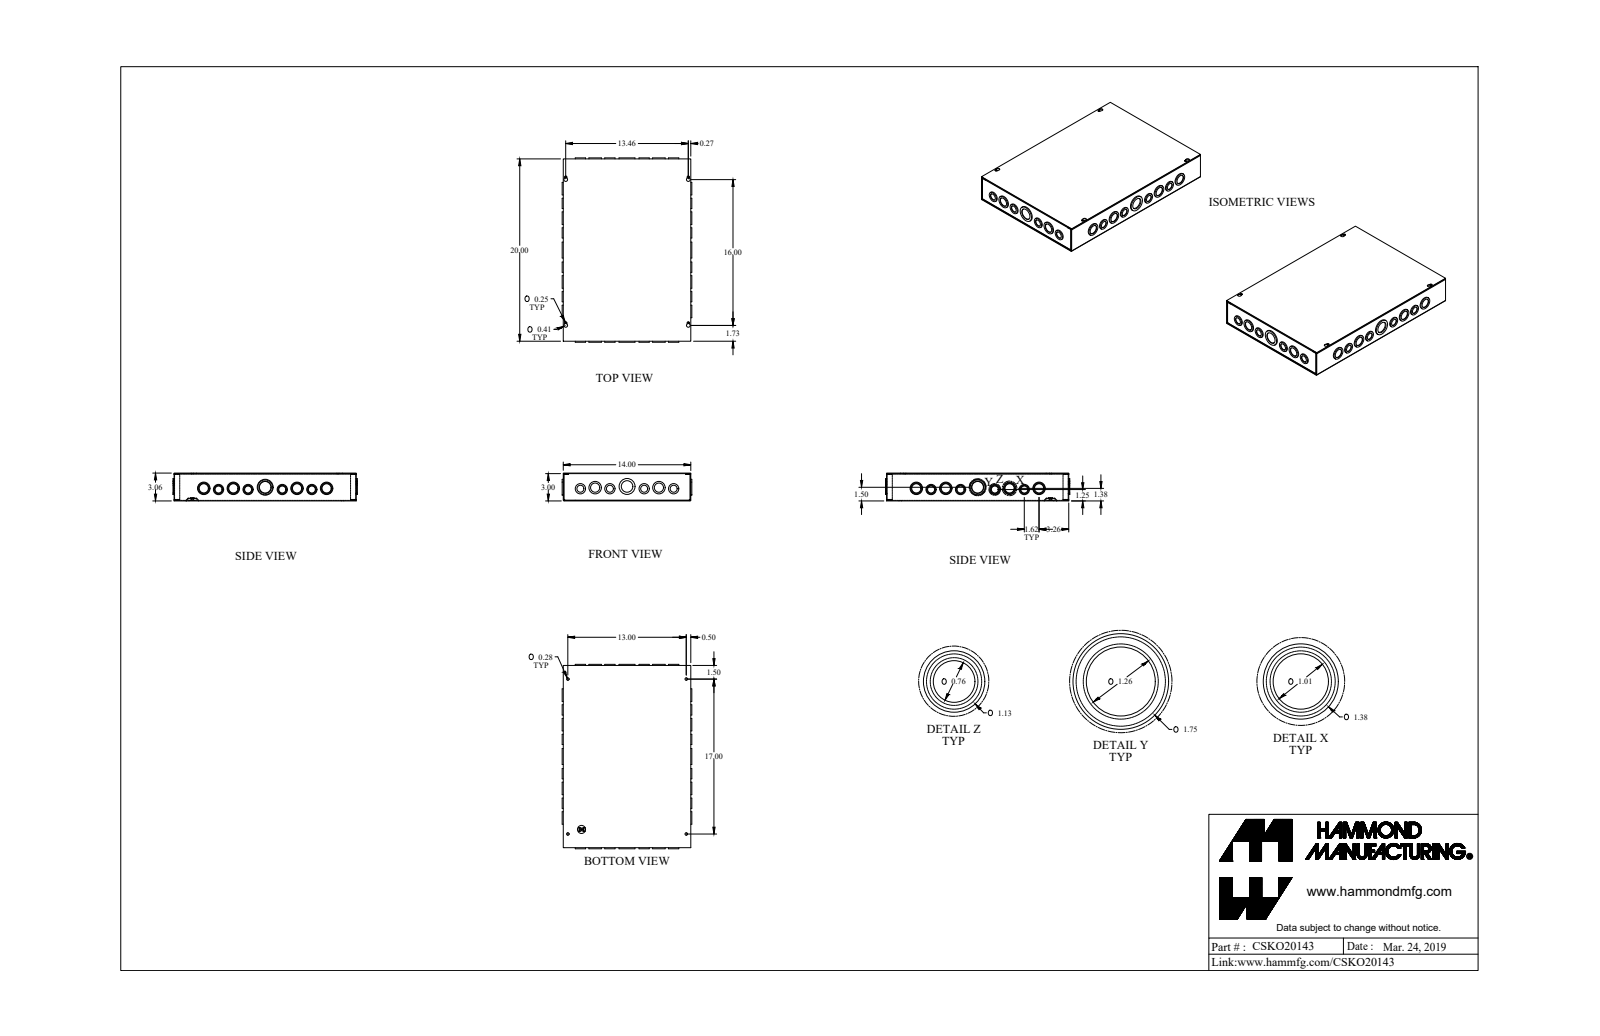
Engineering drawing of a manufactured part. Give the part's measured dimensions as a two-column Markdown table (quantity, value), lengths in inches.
| quantity | value |
| --- | --- |
| part name | CSKO20143_Default |
| STEP written by | SolidWorks 2019 (CONFIG_CONTROL_DESIGN) |
| units | inches |
| bodies | 4 solids, 589 faces (253 planar, 328 cylindrical, 8 other) |
| overall size | 20.234 × 14.234 × 3.057 |
| volume | 47.09 in³ |
| surface area | 1 666 in² |
| round holes (diameter × count) | 1.011 × 14, 0.761 × 8, 1.261 × 8, 0.17 × 5, 0.281 × 4, 1.636 × 2, 0.5 × 1 |
| round bosses / shafts (diameter × count) | 1.125 × 12, 0.875 × 8, 1.375 × 7, 1.125 × 4, 0.875 × 4, 1.75 × 2, 1.375 × 1, 0.492 × 1 |
| partial cylindrical surfaces (radius × count) | 0.029 × 12, 0.086 × 12, 0.057 × 8, 0.125 × 4, 0.203 × 4 |
| main face-to-face distances | 0.057, 3, 2.943, 3.057, 13.943, 14, 19.943, 13.886, 0.114, 20 |
| hole center spacings | 1.625, 3.24, 7, 8.621, 0.55, 1.896, 3.502, 5.126 |
